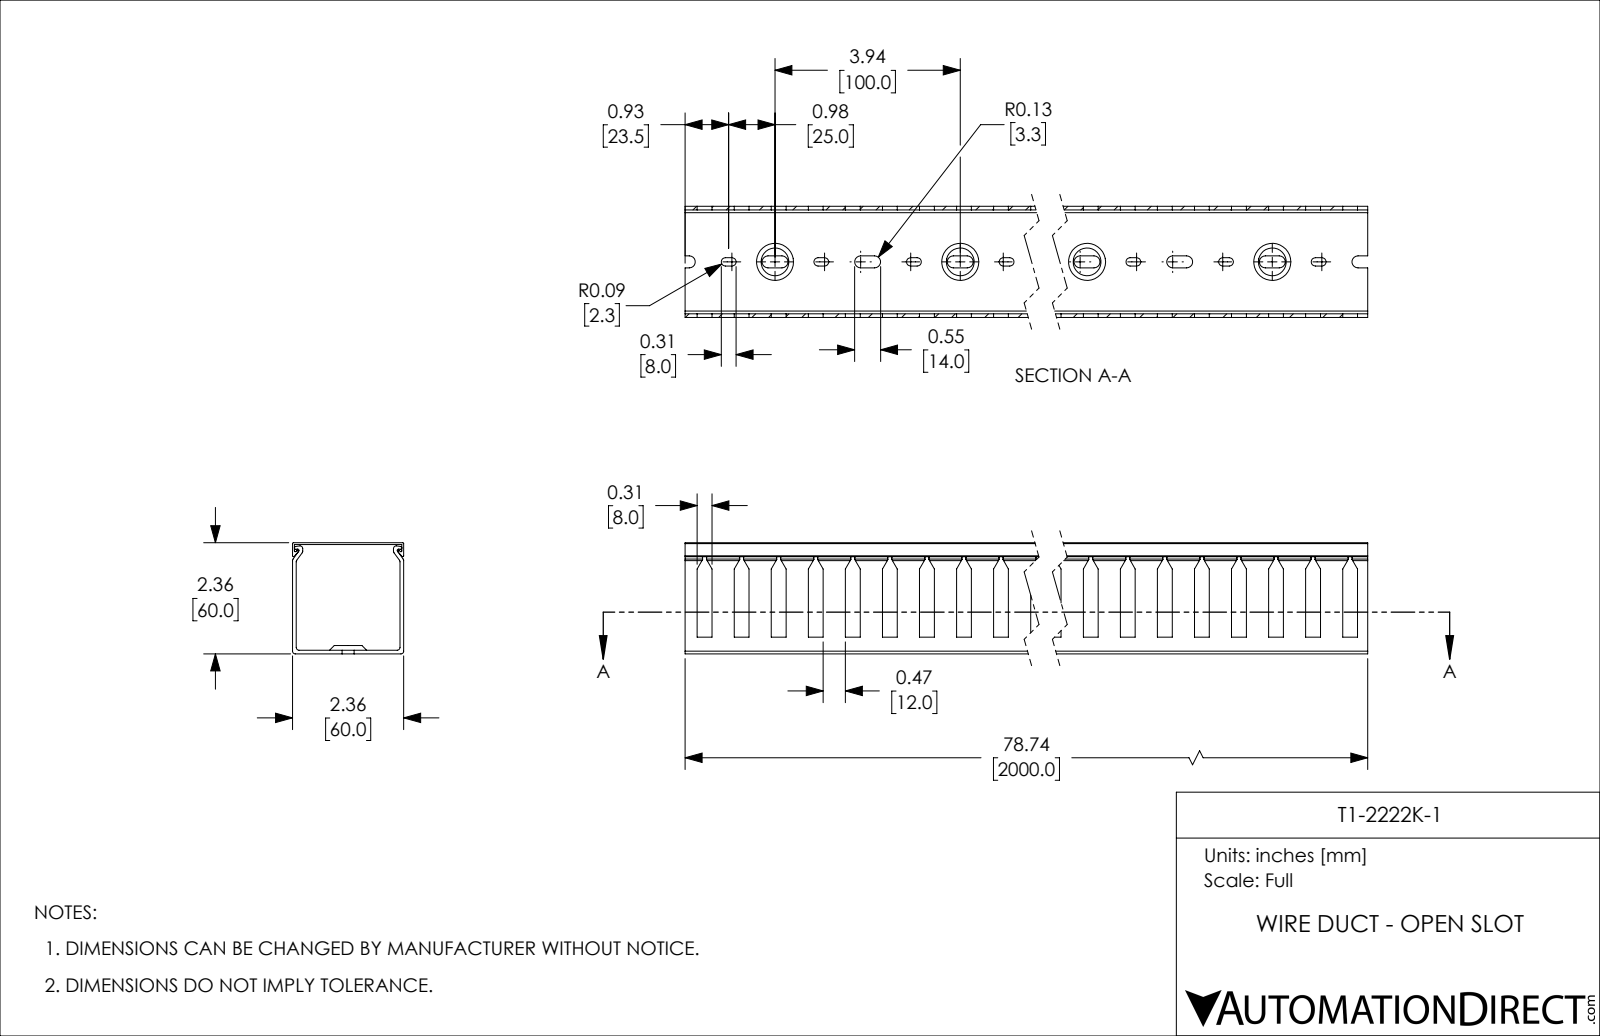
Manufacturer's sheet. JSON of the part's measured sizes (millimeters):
{"part_name": "T1-2222K-1", "step_written_by": "SolidWorks 2021 (CONFIG_CONTROL_DESIGN)", "units": "millimeters", "bodies": {"solids": 2, "faces": 1005, "planar": 534, "cylindrical": 431, "other": 40}, "overall_size": [2000, 60, 60], "volume_mm3": 854712, "surface_area_mm2": 1012000, "partial_cylinders_radius": [[2.25, 80], [3.25, 80], [1.5, 12], [0.5, 8], [0.75, 6]], "face_to_face_distances": [2, 58, 60, 1, 59, 57, 56, 4.5, 54.5, 5.5]}
